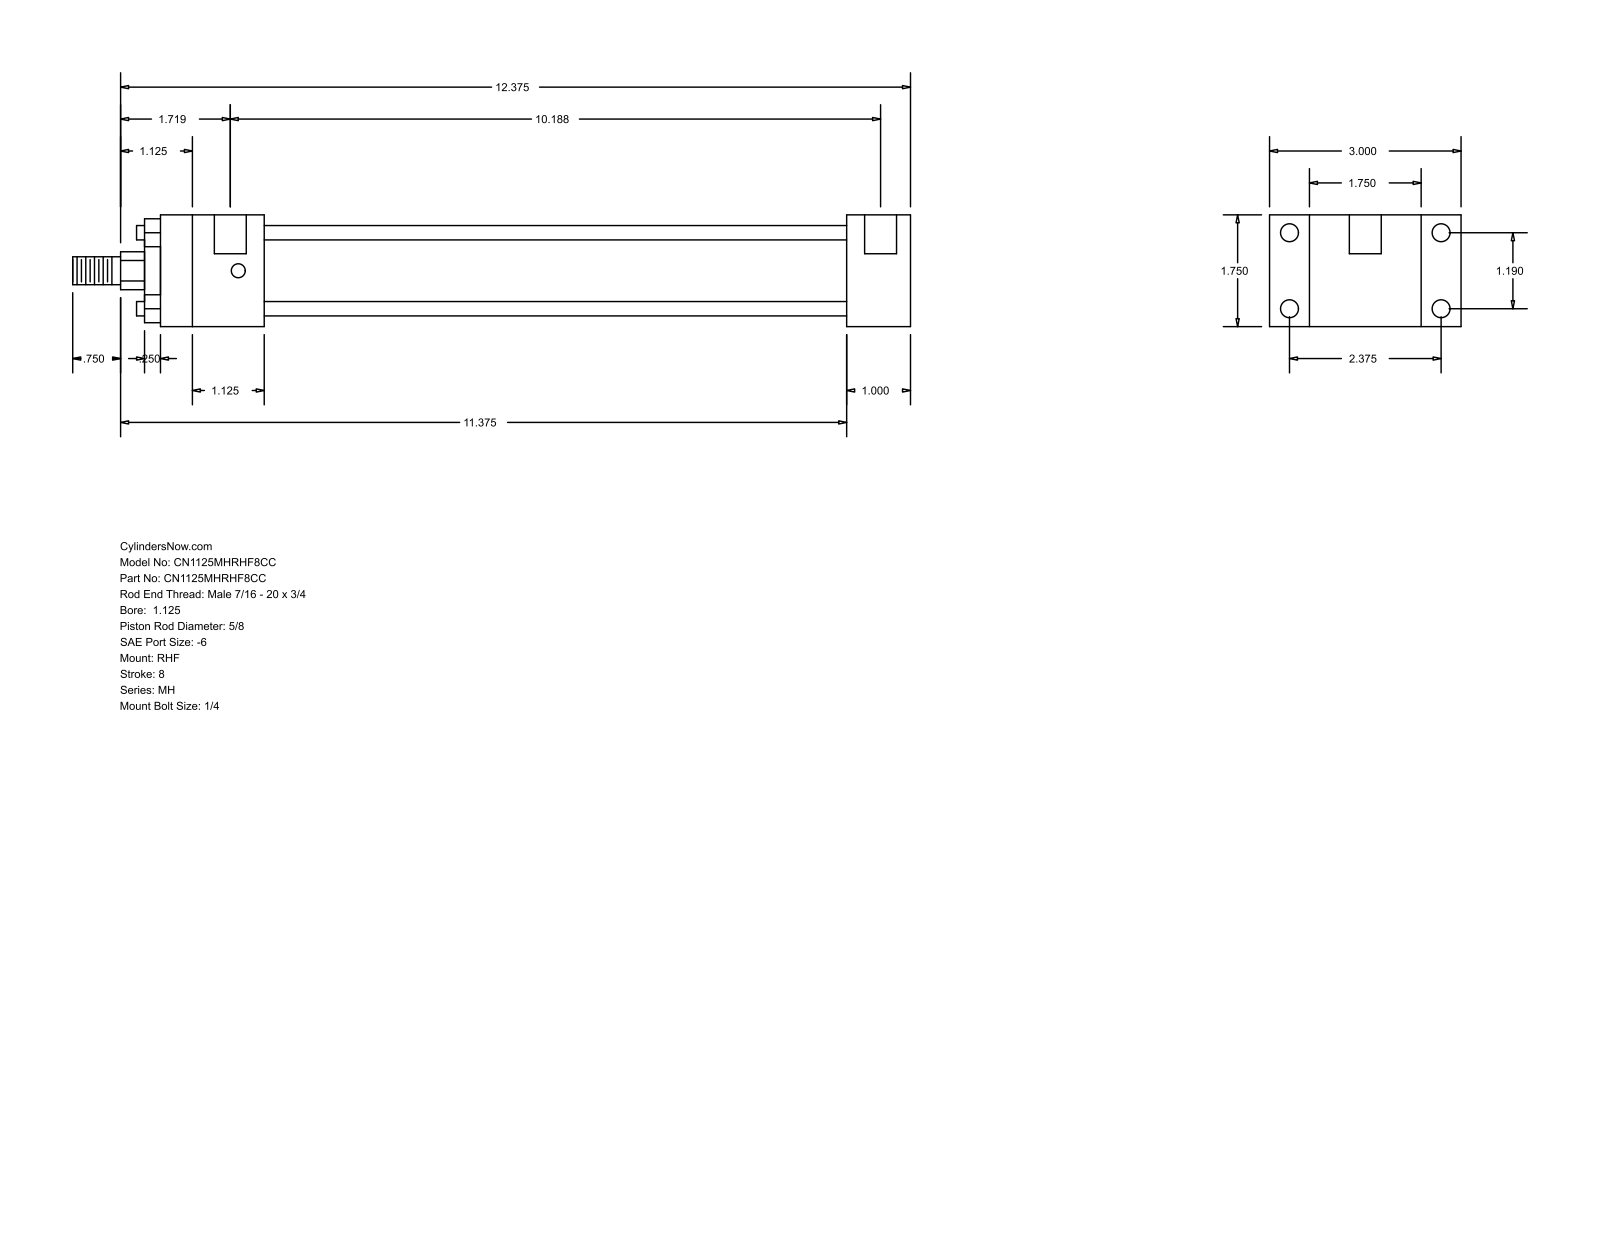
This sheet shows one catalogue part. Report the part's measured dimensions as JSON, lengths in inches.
{"part_name": "MH_RHF__0112_0.625", "step_written_by": "GSSL Pune (CONFIG_CONTROL_DESIGN)", "units": "inches", "bodies": {"solids": 0, "faces": 88, "planar": 60, "cylindrical": 28, "other": 0}, "overall_size": [13.125, 3, 1.75], "round_holes": [[0.219, 4], [0.281, 4], [0.5, 2]], "round_bosses_or_shafts": [[0.225, 4], [1.375, 1], [1.125, 1], [0.625, 1], [0.437, 1]], "partial_cylinders_radius": [[0.297, 1]], "face_to_face_distances": [1.75, 0.625, 2.375, 1, 3, 9.125, 10.125, 1.625, 10.75, 11.75], "hole_center_spacings": [1.19, 2.375, 2.656, 10.063, 0.125, 10.187]}
